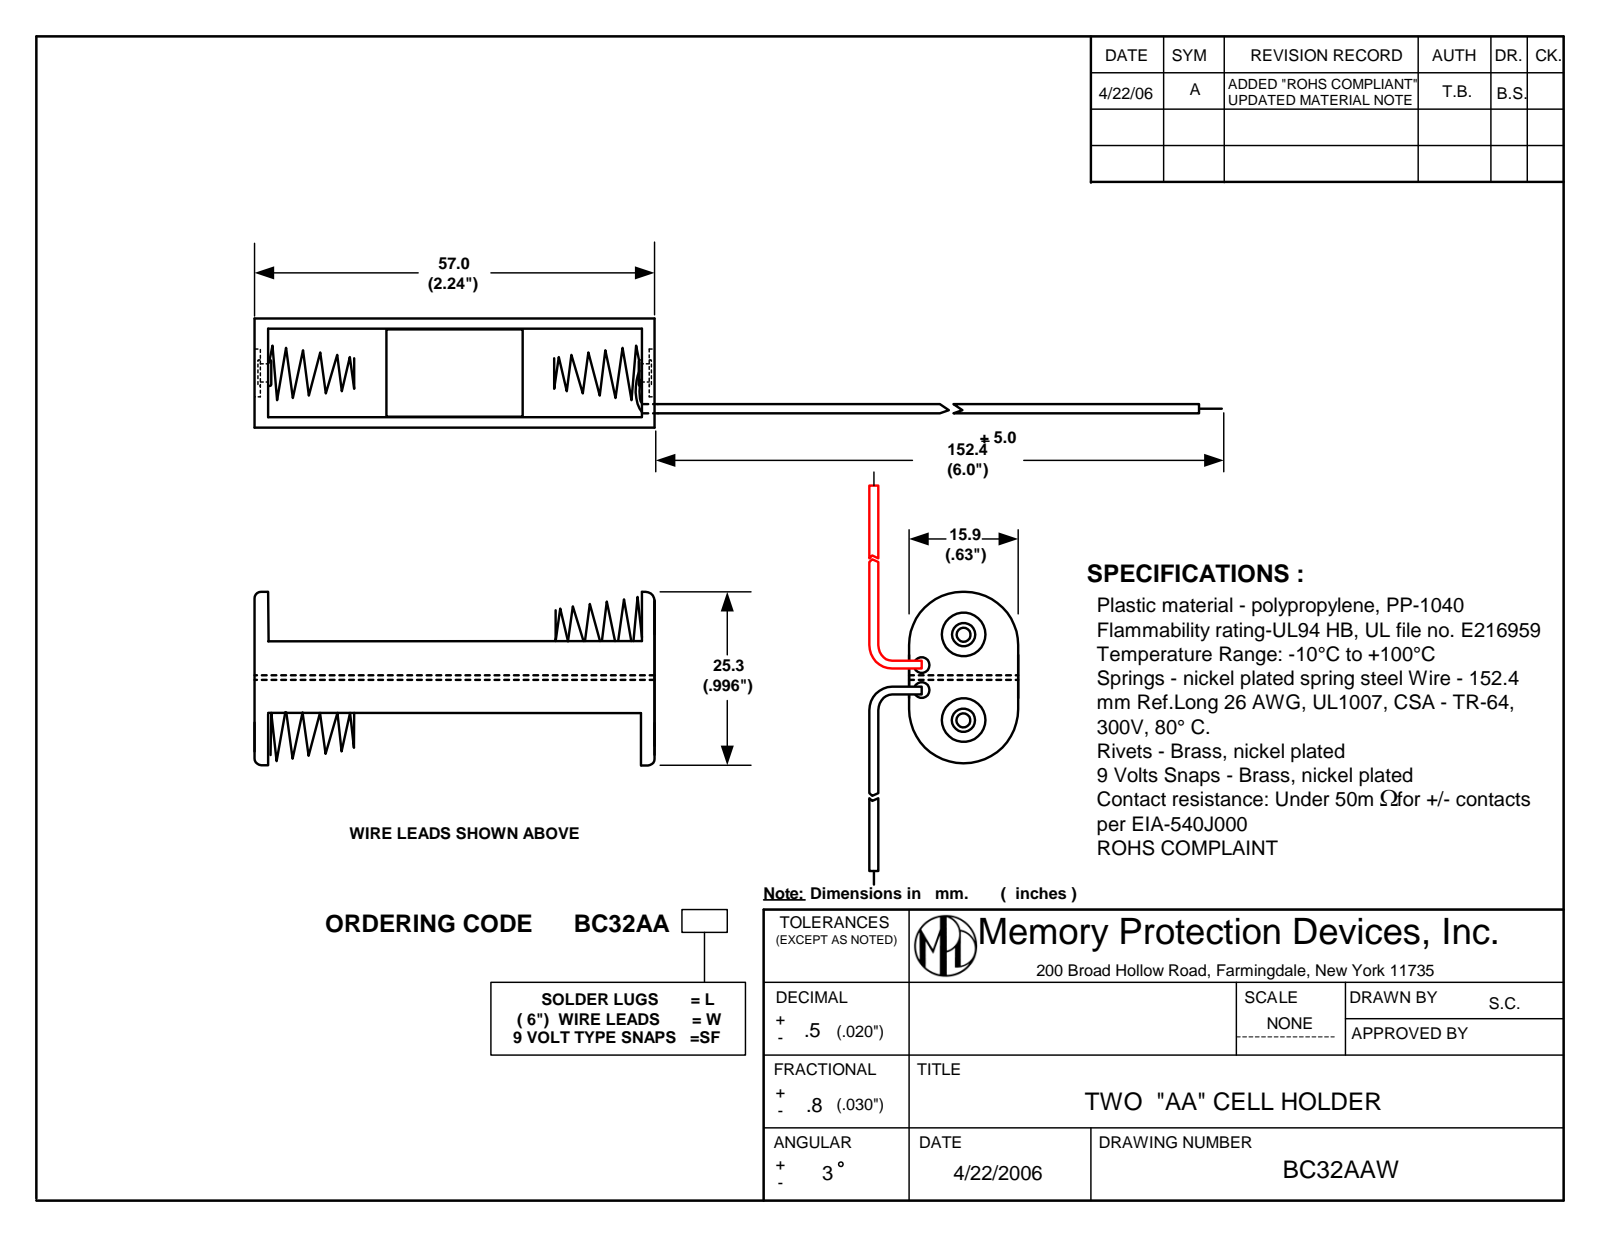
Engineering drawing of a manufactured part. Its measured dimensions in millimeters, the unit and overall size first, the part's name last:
Units: millimetres
Overall size (bounding box): 212 × 25 × 15.9
Round holes (diameter × count): ⌀0.4 ×2, ⌀2 ×2, ⌀2.3 ×2, ⌀2.54 ×2, ⌀9.5 ×2
Round bosses / shafts (diameter × count): ⌀6.2 ×2, ⌀5 ×2, ⌀3.8 ×2, ⌀0.81 ×2, ⌀0.63 ×1
Partial cylindrical surfaces — rounded edges, fillets, slot ends (radius × count): R7.5 ×4, R0.32 ×1
Main face-to-face distances: 1.3, 14.6, 15.9, 13.3, 55.7, 54.4, 0.31, 56.69, 0.99, 55.39
Hole centre spacings: 7.48, 10.23, 3.84, 12.7
Volume: 3 584 mm³ · Surface area: 7 864 mm²
Bodies: 9 solids, 266 faces (118 planar, 88 cylindrical, 60 other)
Part name (STEP PRODUCT): BC32AAW
STEP written by: SolidWorks 2016 (AUTOMOTIVE_DESIGN)
